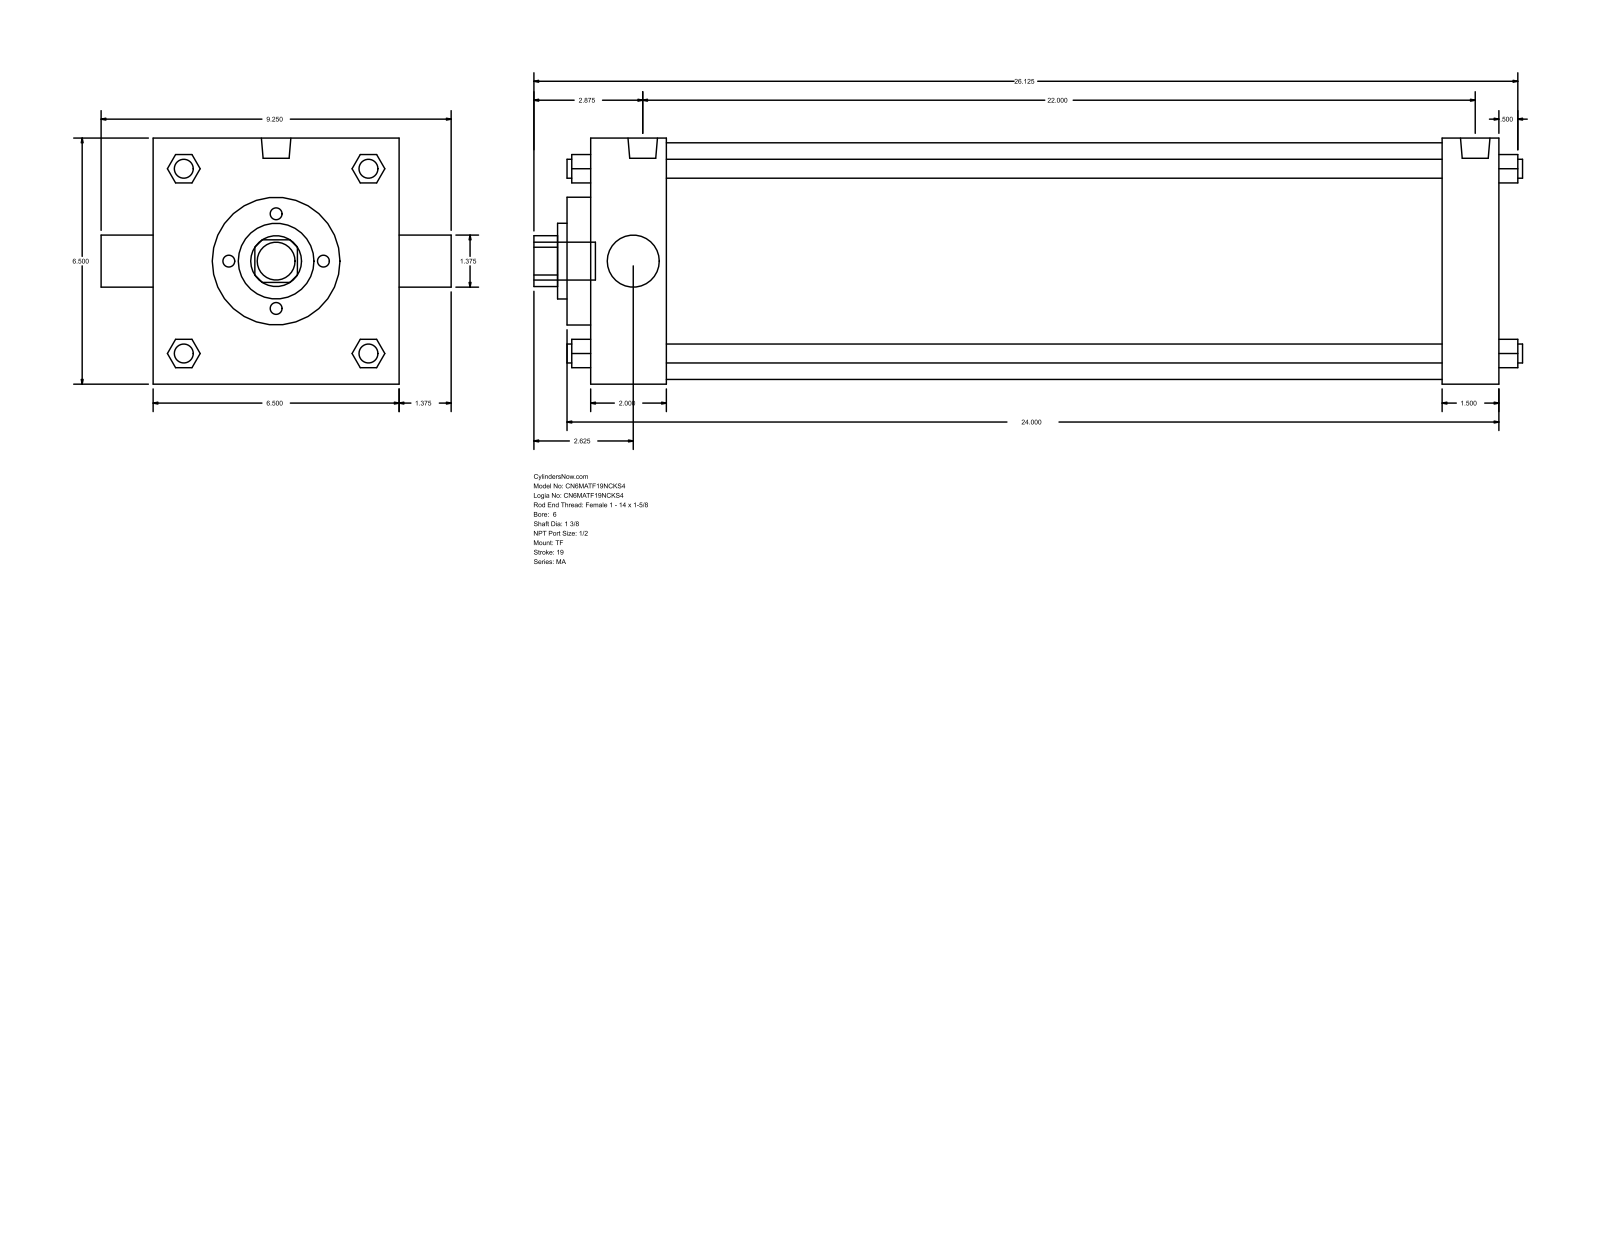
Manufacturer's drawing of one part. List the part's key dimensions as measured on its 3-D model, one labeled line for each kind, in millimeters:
Part name (STEP PRODUCT): MA_TF__0600_1.375
STEP written by: GSSL Pune (CONFIG_CONTROL_DESIGN)
Units: millimetres
Bodies: 0 solids, 122 faces (93 planar, 29 cylindrical, 0 other)
Overall size (bounding box): 663.58 × 234.95 × 165.1
Round holes (diameter × count): ⌀34.92 ×2, ⌀50.8 ×1, ⌀85.72 ×1, ⌀158.75 ×1
Round bosses / shafts (diameter × count): ⌀12.7 ×4, ⌀17.46 ×3, ⌀19.77 ×2, ⌀25.4 ×1
Partial cylindrical surfaces — rounded edges, fillets, slot ends (radius × count): R17.06 ×1
Main face-to-face distances: 165.1, 612.78, 50.8, 561.98, 574.67, 523.87, 38.11, 15.87, 66.67, 590.54
